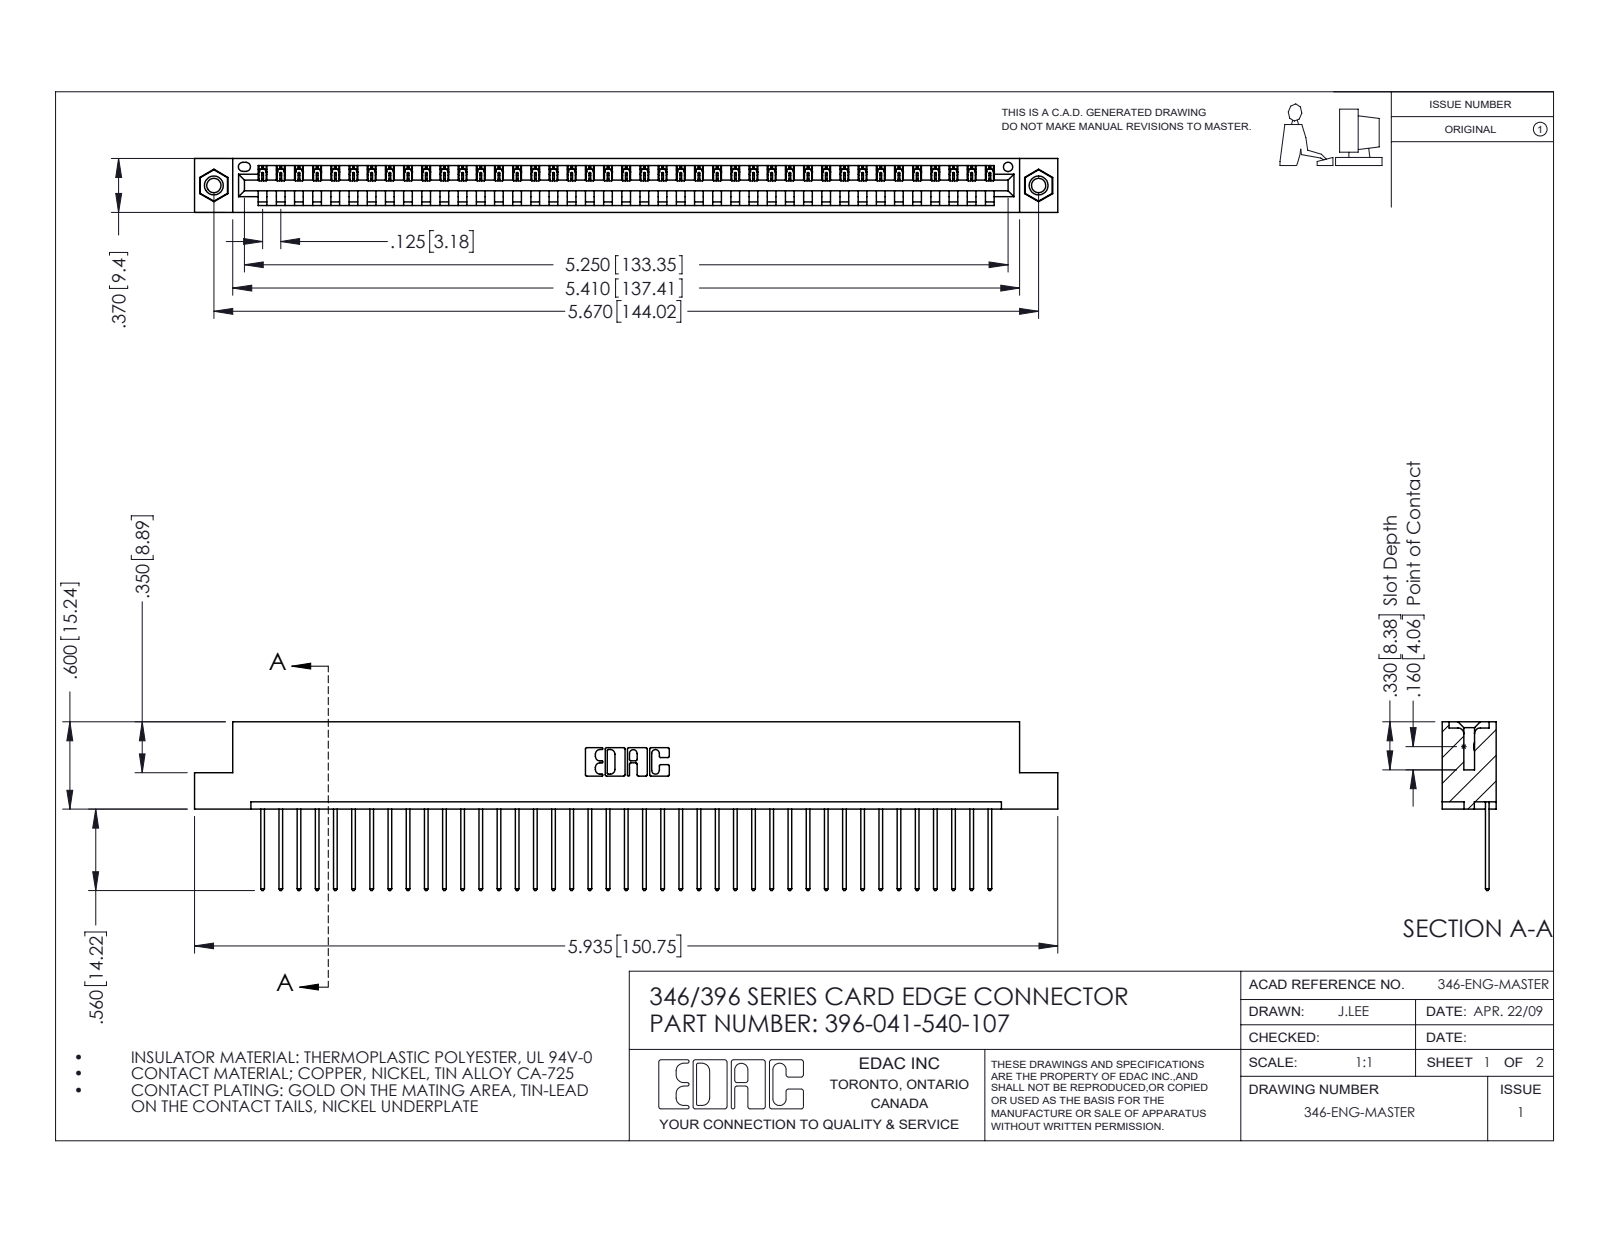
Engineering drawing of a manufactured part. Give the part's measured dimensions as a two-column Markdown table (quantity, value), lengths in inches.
| quantity | value |
| --- | --- |
| part name | 396-041-540-107; 345-292-001_345-293-140; 346 Part_Flush Mounting Lugs - 0.156 Dia-TI; 345-250-001_345-250-005-103 |
| STEP written by | SolidWorks 2016 (CONFIG_CONTROL_DESIGN) |
| units | inches |
| bodies | 44 solids, 2560 faces (1748 planar, 796 cylindrical, 16 other) |
| overall size | 5.935 × 1.16 × 0.37 |
| volume | 0.883 in³ |
| surface area | 28.69 in² |
| round holes (diameter × count) | 0.098 × 2, 0.125 × 2, 0.156 × 2, 0.064 × 1 |
| round bosses / shafts (diameter × count) | 0.155 × 2 |
| partial cylindrical surfaces (radius × count) | 0.006 × 82, 0.01 × 82, 0.01 × 22, 0.007 × 6, 0.031 × 6, 0.026 × 3, 0.031 × 2, 0.04 × 2 |
| main face-to-face distances | 0.048, 0.322, 0.37, 0.25, 0.072, 0.298, 0.025, 0.148, 0.222, 0.1 |
| hole center spacings | 0.246, 5.461, 5.67 |
